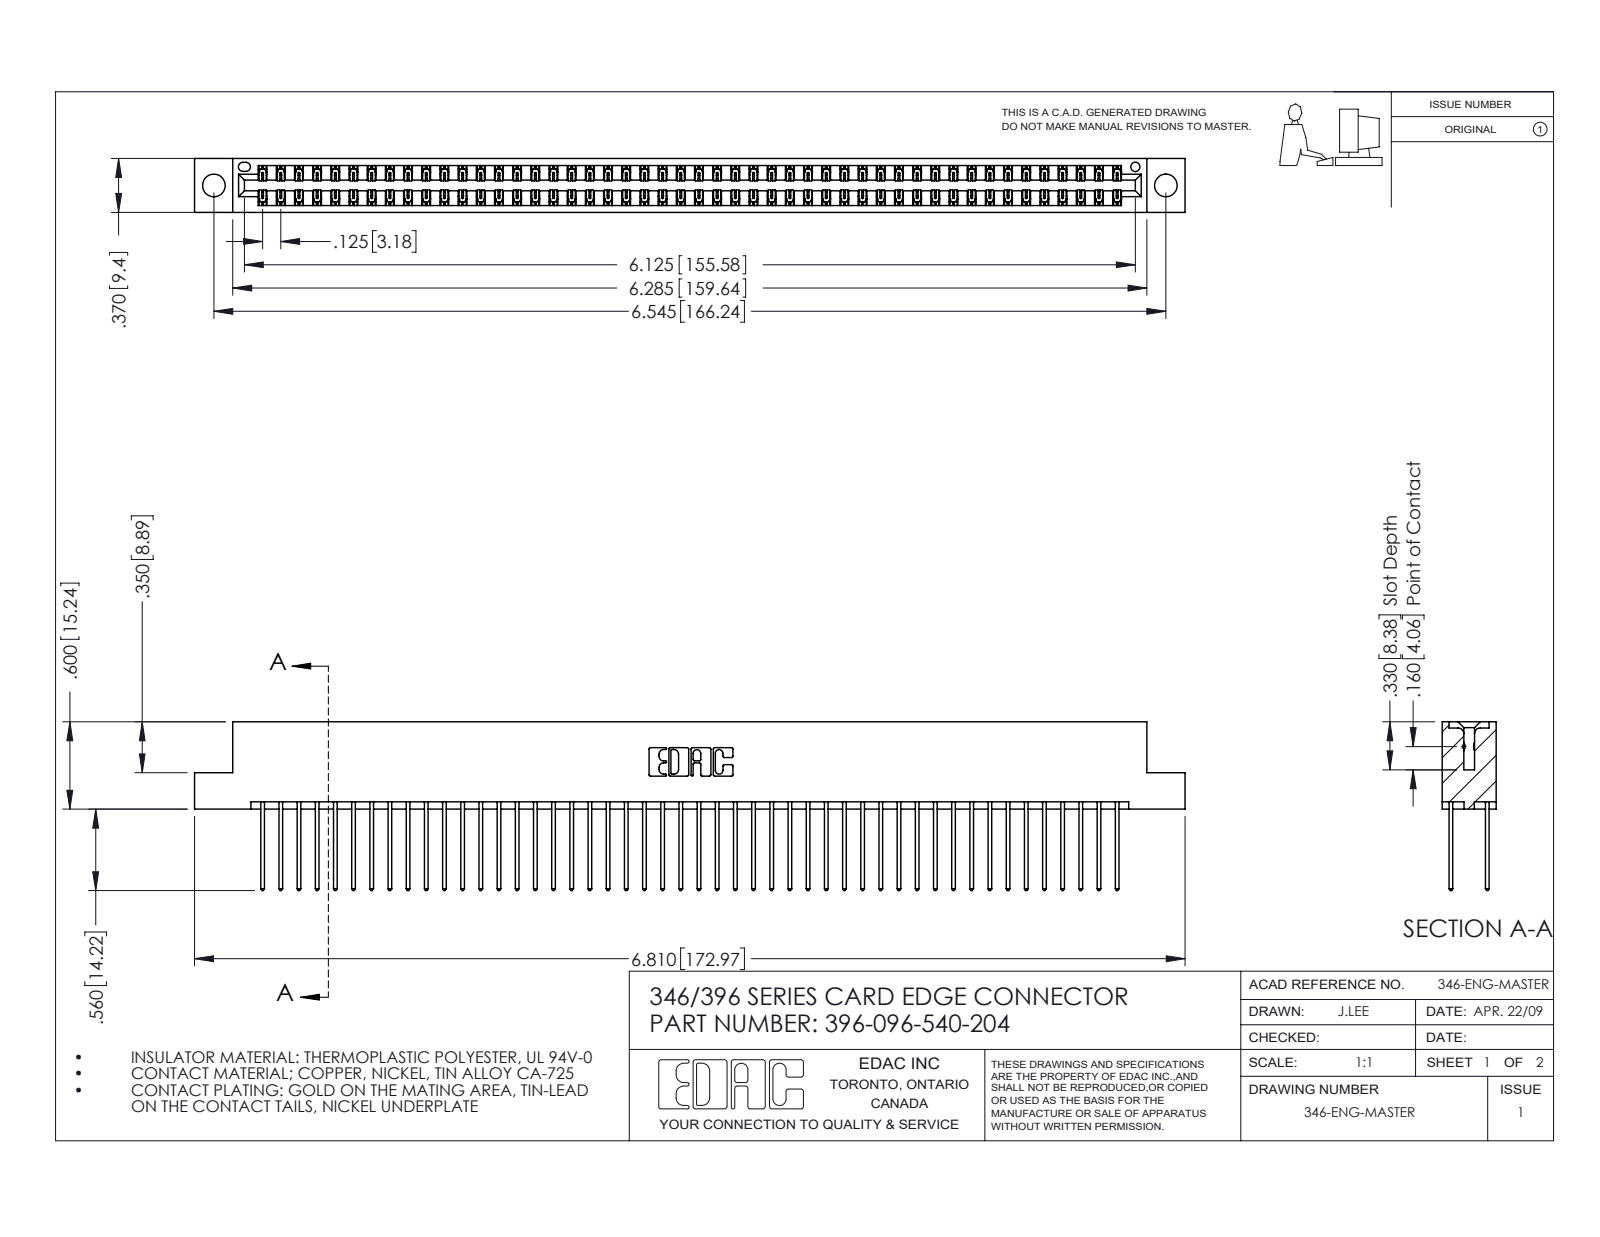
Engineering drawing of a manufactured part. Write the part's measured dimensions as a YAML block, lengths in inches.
part_name: "346 Part_Flush Mounting Lugs - 0.156 Dia-TH; 396-096-540-204; 345-292-001_345-293-140"
step_written_by: "SolidWorks 2016 (CONFIG_CONTROL_DESIGN)"
units: inches
bodies: {solids: 97, faces: 5114, planar: 3436, cylindrical: 1678, other: 0}
overall_size: [6.81, 1.16, 0.37]
volume: 1.049
surface_area: 39.15
round_holes:
  - {diameter: 0.156, count: 2}
  - {diameter: 0.064, count: 1}
partial_cylinders:
  - {radius: 0.006, count: 144}
  - {radius: 0.01, count: 96}
  - {radius: 0.01, count: 22}
  - {radius: 0.007, count: 6}
  - {radius: 0.031, count: 6}
  - {radius: 0.026, count: 3}
  - {radius: 0.014, count: 2}
  - {radius: 0.022, count: 2}
face_to_face_distances: [0.048, 0.322, 0.25, 0.072, 0.298, 0.025, 0.37, 0.275, 0.148, 0.222]
hole_center_spacings: [0.246, 6.336, 6.545]
